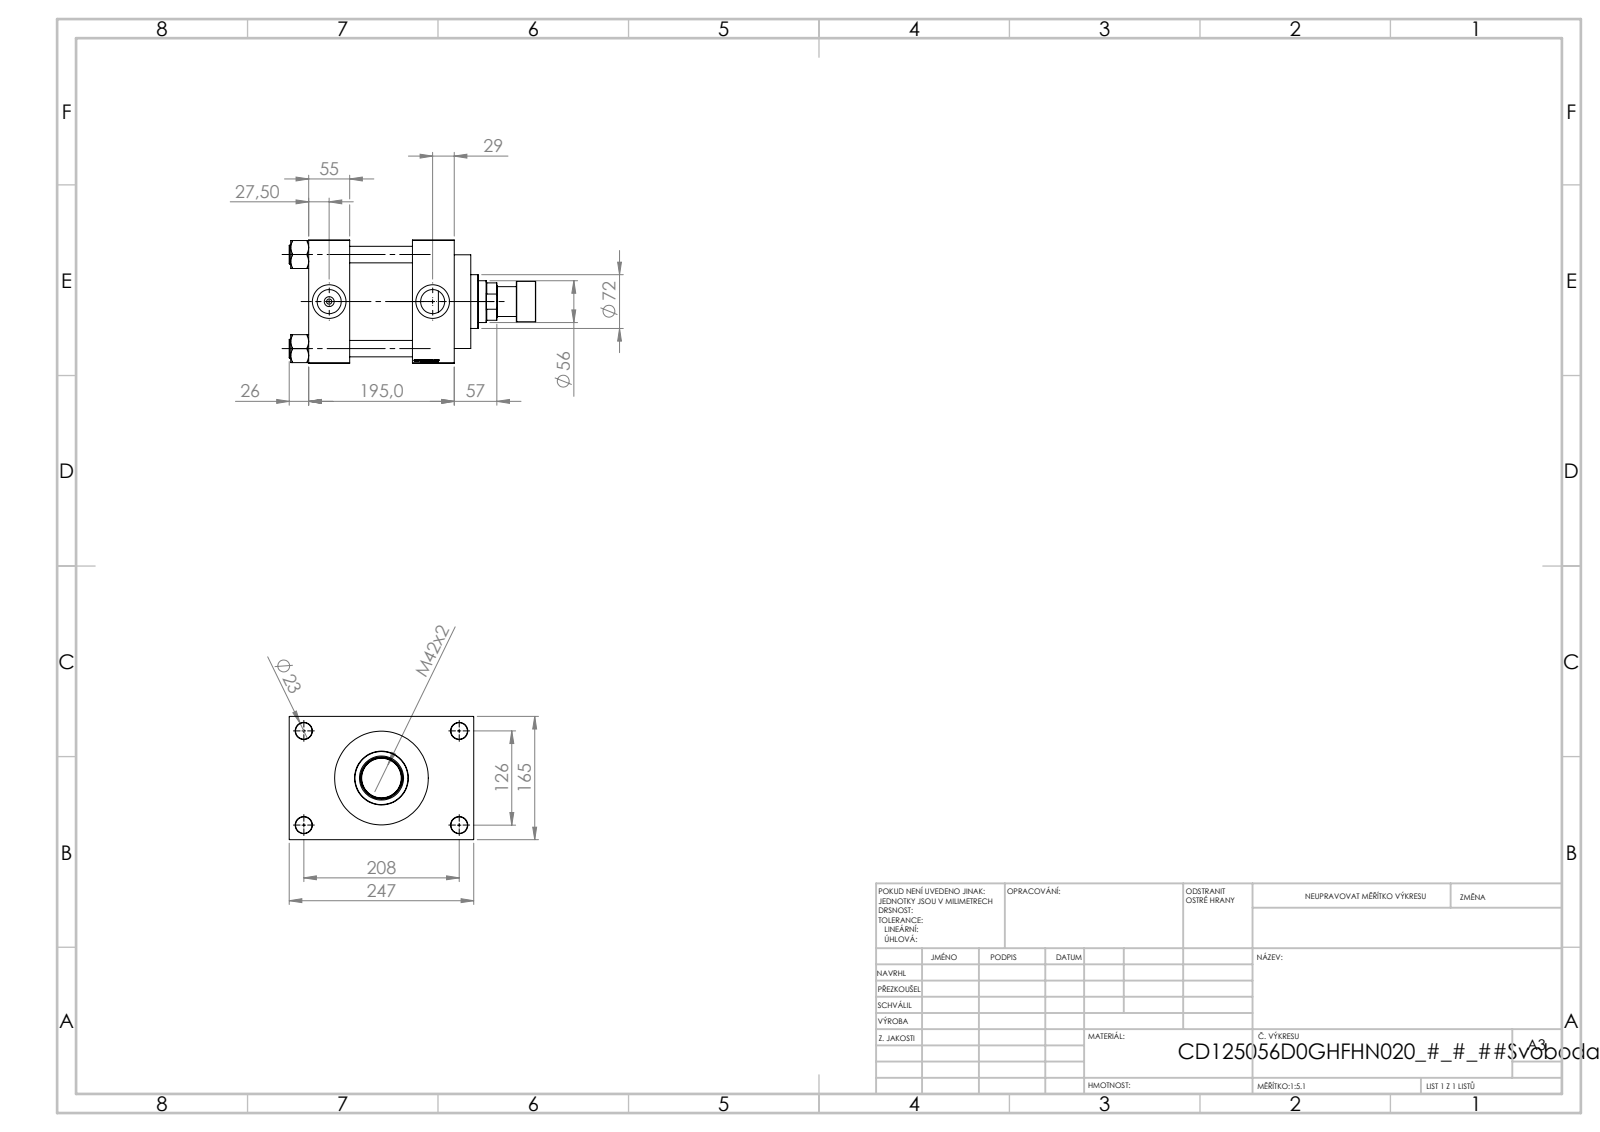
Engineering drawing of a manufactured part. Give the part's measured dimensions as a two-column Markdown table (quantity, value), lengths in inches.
| quantity | value |
| --- | --- |
| part name | V215CR_ROD_END_F; V215CD_VCP_D; V215CD_D_TYCINKA; V215CD_NUT_M5_D (+2 more) |
| STEP written by | SolidWorks 2019 (CONFIG_CONTROL_DESIGN) |
| units | inches |
| bodies | 12 solids, 1162 faces (548 planar, 90 cylindrical, 524 other) |
| overall size | 12.992 × 9.724 × 6.496 |
| volume | 306.2 in³ |
| surface area | 847.2 in² |
| round holes (diameter × count) | 0.866 × 8, 0.276 × 2, 1.269 × 2, 1.772 × 2, 1.594 × 1, 2.205 × 1, 2.323 × 1, 3.78 × 1, 4.921 × 1, 4.941 × 1 |
| round bosses / shafts (diameter × count) | 0.984 × 4, 5.157 × 1, 2.835 × 1, 2.126 × 1, 1.575 × 1 |
| main face-to-face distances | 6.496, 5.472, 3.307, 2.165, 2.205, 7.677, 5.512, 1.614, 8.11, 6.84 |
| hole center spacings | 1.616, 3.505, 4.787, 4.957, 5.215, 6.573, 8.233, 4.961 |
